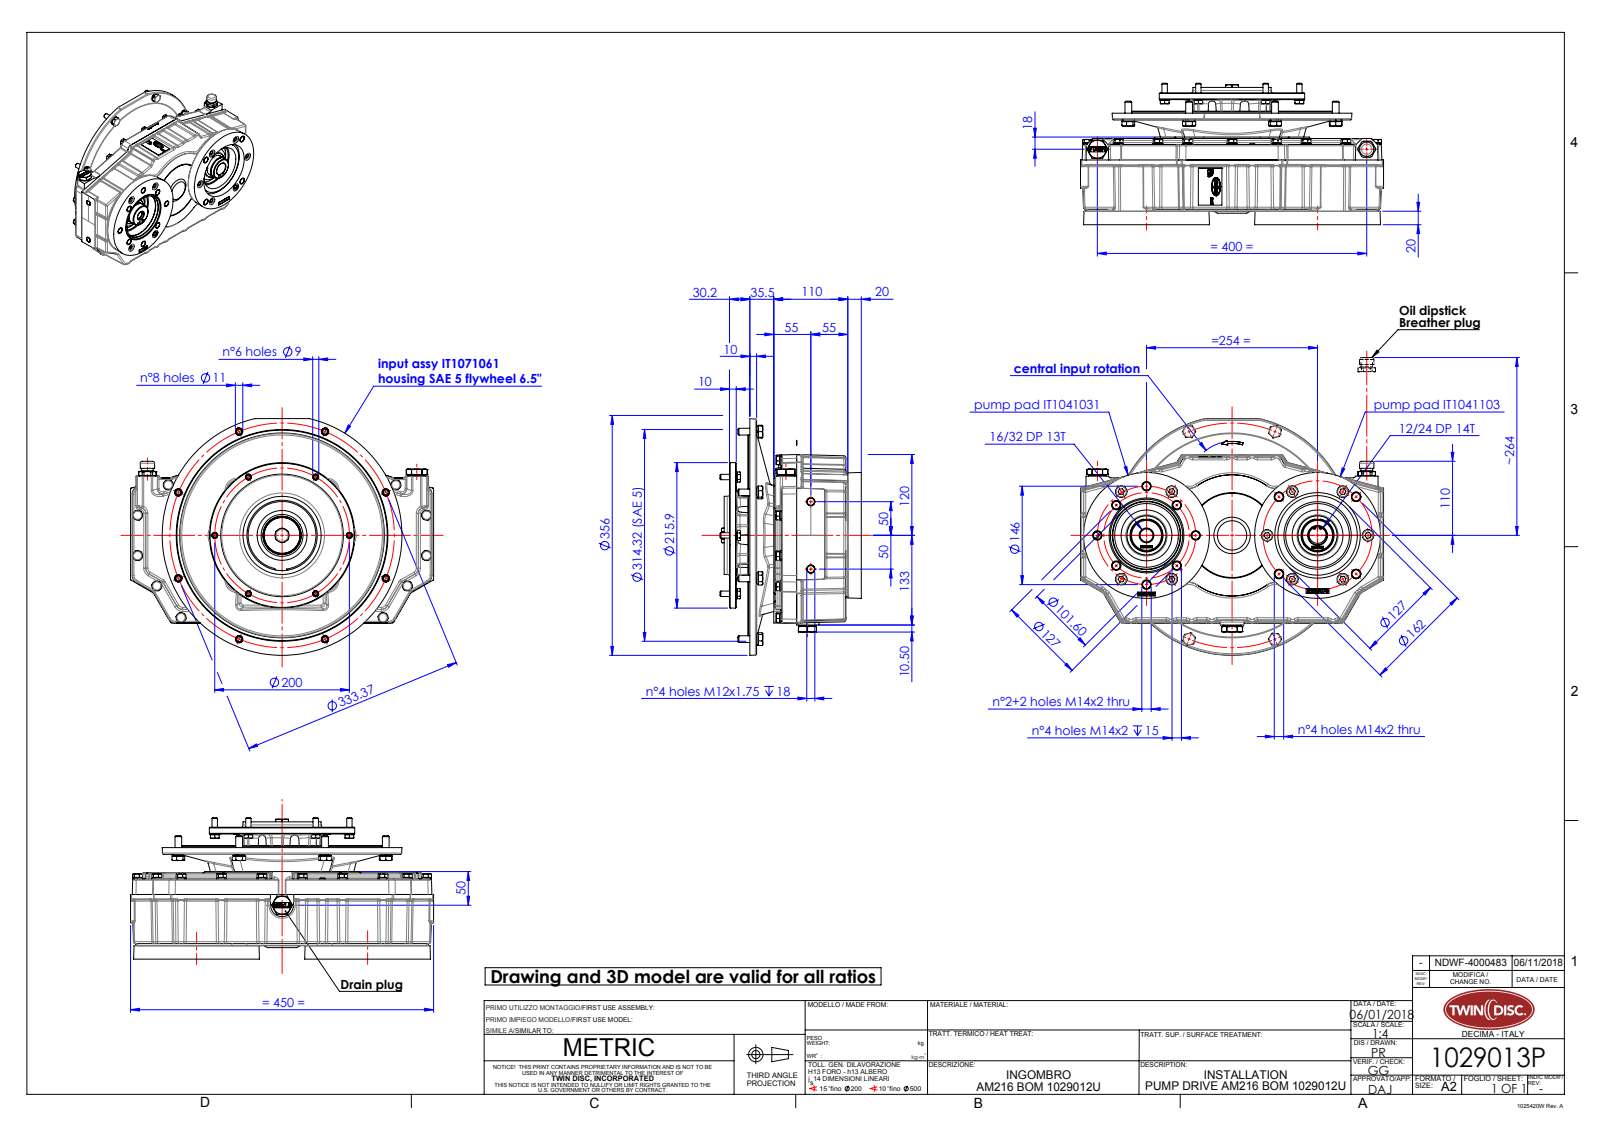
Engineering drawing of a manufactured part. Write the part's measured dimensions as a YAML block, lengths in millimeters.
part_name: "1029013P; IT1041103_rev00-installation; IT1041031_rev00-installation; IT1071061-installation (+4 more)"
step_written_by: "SolidWorks 2015 (AUTOMOTIVE_DESIGN)"
units: millimeters
bodies: {solids: 71, faces: 4823, planar: 2232, cylindrical: 1079, other: 1512}
overall_size: [450, 351.3, 209.9]
volume: 3398000
surface_area: 1693000
round_holes:
  - {diameter: 9, count: 25}
  - {diameter: 11, count: 25}
  - {diameter: 8.2, count: 19}
  - {diameter: 8.8, count: 19}
  - {diameter: 12, count: 14}
  - {diameter: 10.2, count: 13}
  - {diameter: 17, count: 10}
  - {diameter: 18, count: 7}
  - {diameter: 8.4, count: 6}
  - {diameter: 10, count: 5}
  - {diameter: 14, count: 4}
  - {diameter: 8, count: 3}
round_bosses_or_shafts:
  - {diameter: 12.2, count: 25}
  - {diameter: 8, count: 25}
  - {diameter: 10, count: 23}
  - {diameter: 14.8, count: 19}
  - {diameter: 16, count: 15}
  - {diameter: 18.1, count: 8}
  - {diameter: 16.2, count: 8}
  - {diameter: 14, count: 8}
partial_cylinders:
  - {radius: 3, count: 93}
  - {radius: 2, count: 28}
  - {radius: 2.5, count: 24}
  - {radius: 1.5, count: 10}
  - {radius: 5, count: 10}
  - {radius: 11, count: 8}
  - {radius: 10, count: 6}
  - {radius: 16, count: 6}
face_to_face_distances: [76, 96, 108, 32, 21.5, 23, 34, 0.5, 10.5, 97.5]
hole_center_spacings: [60, 75, 57.4, 91.02, 92.5, 106.06, 120, 138.58]
